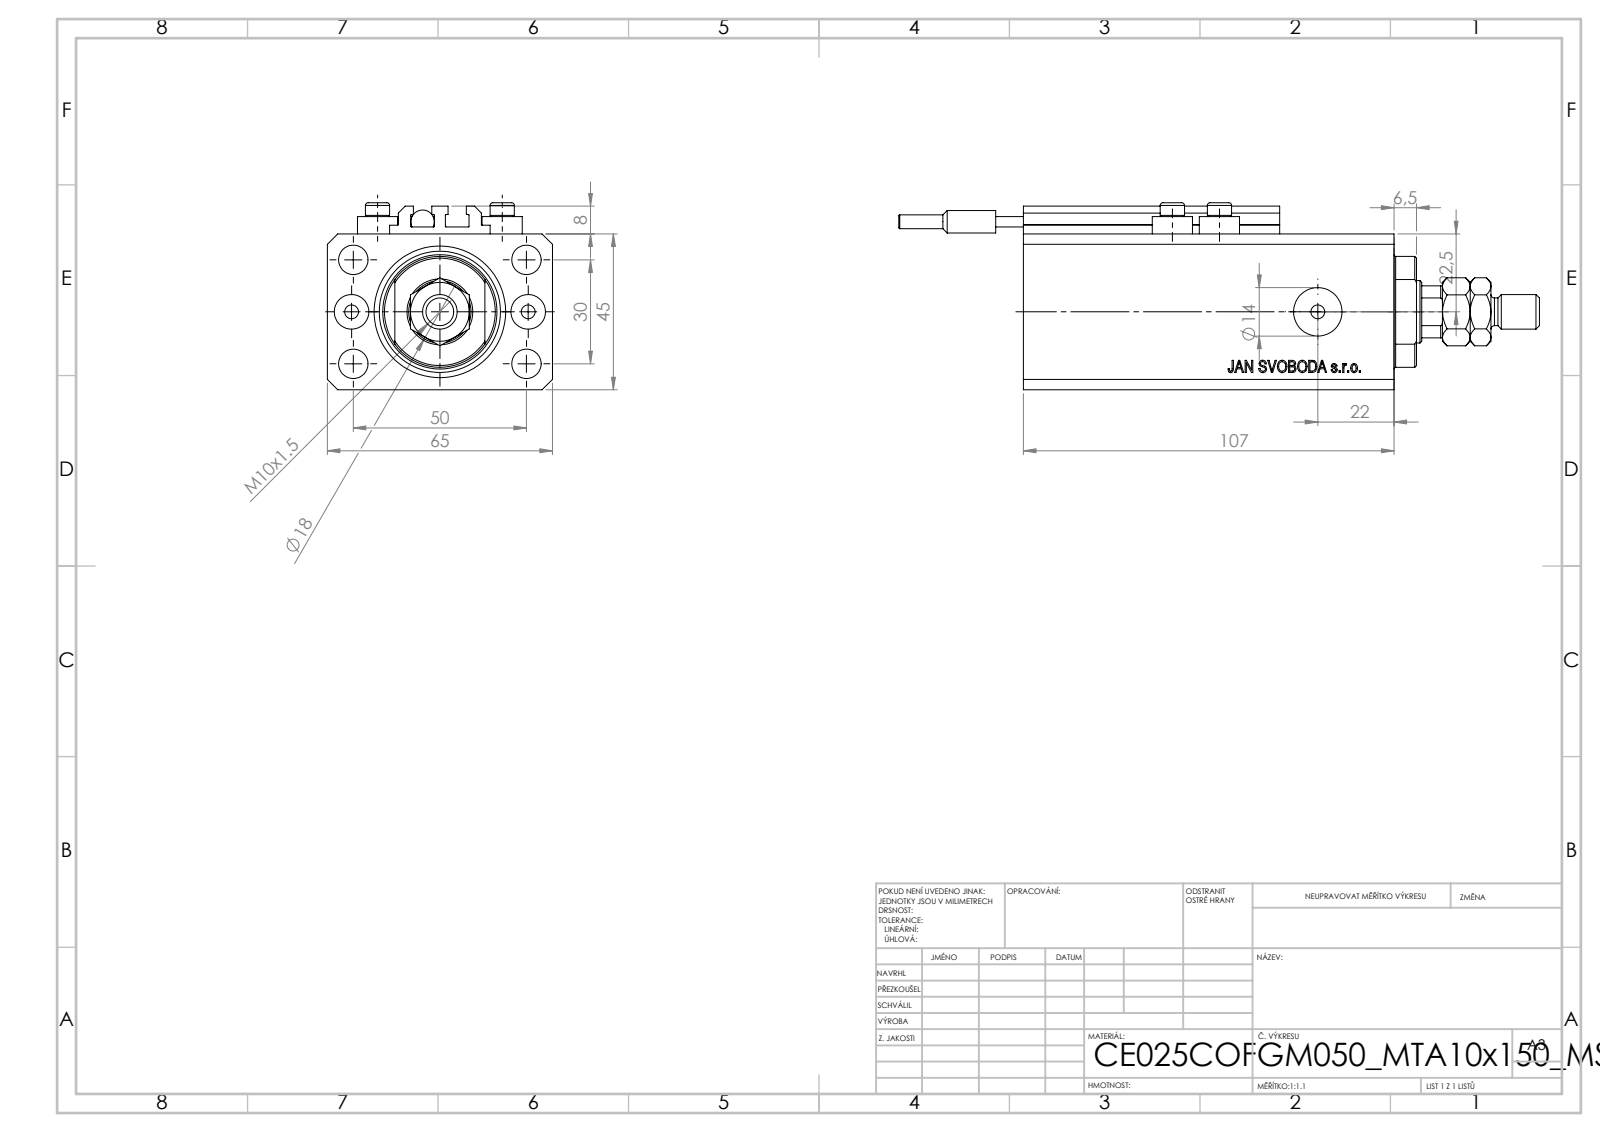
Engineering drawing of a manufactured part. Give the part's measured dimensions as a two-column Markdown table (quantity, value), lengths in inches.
| quantity | value |
| --- | --- |
| part name | ALLEN BOLT V250CE; V250CE_C_Body; V250CE_VC_C; V250CE_C_VCP (+2 more) |
| STEP written by | SolidWorks 2019 (CONFIG_CONTROL_DESIGN) |
| units | inches |
| bodies | 10 solids, 1109 faces (535 planar, 96 cylindrical, 478 other) |
| overall size | 7.283 × 2.559 × 2.126 |
| volume | 18.02 in³ |
| surface area | 119.4 in² |
| round holes (diameter × count) | 0.157 × 8, 0.335 × 5, 0.394 × 2, 0.551 × 2, 0.709 × 1, 0.984 × 1, 1.496 × 1 |
| round bosses / shafts (diameter × count) | 0.457 × 4, 0.276 × 4, 0.394 × 1, 0.315 × 1, 0.268 × 1, 0.256 × 1, 0.157 × 1 |
| partial cylindrical surfaces (radius × count) | 0.008 × 10, 0.335 × 1, 0.63 × 1 |
| main face-to-face distances | 1.772, 2.559, 0.551, 1.85, 3.661, 4.213, 0.118, 0.272, 0.807, 0.079 |
| hole center spacings | 0.591, 1.148, 2.074, 0.535, 1.004, 1.181, 1.417, 1.515 |
